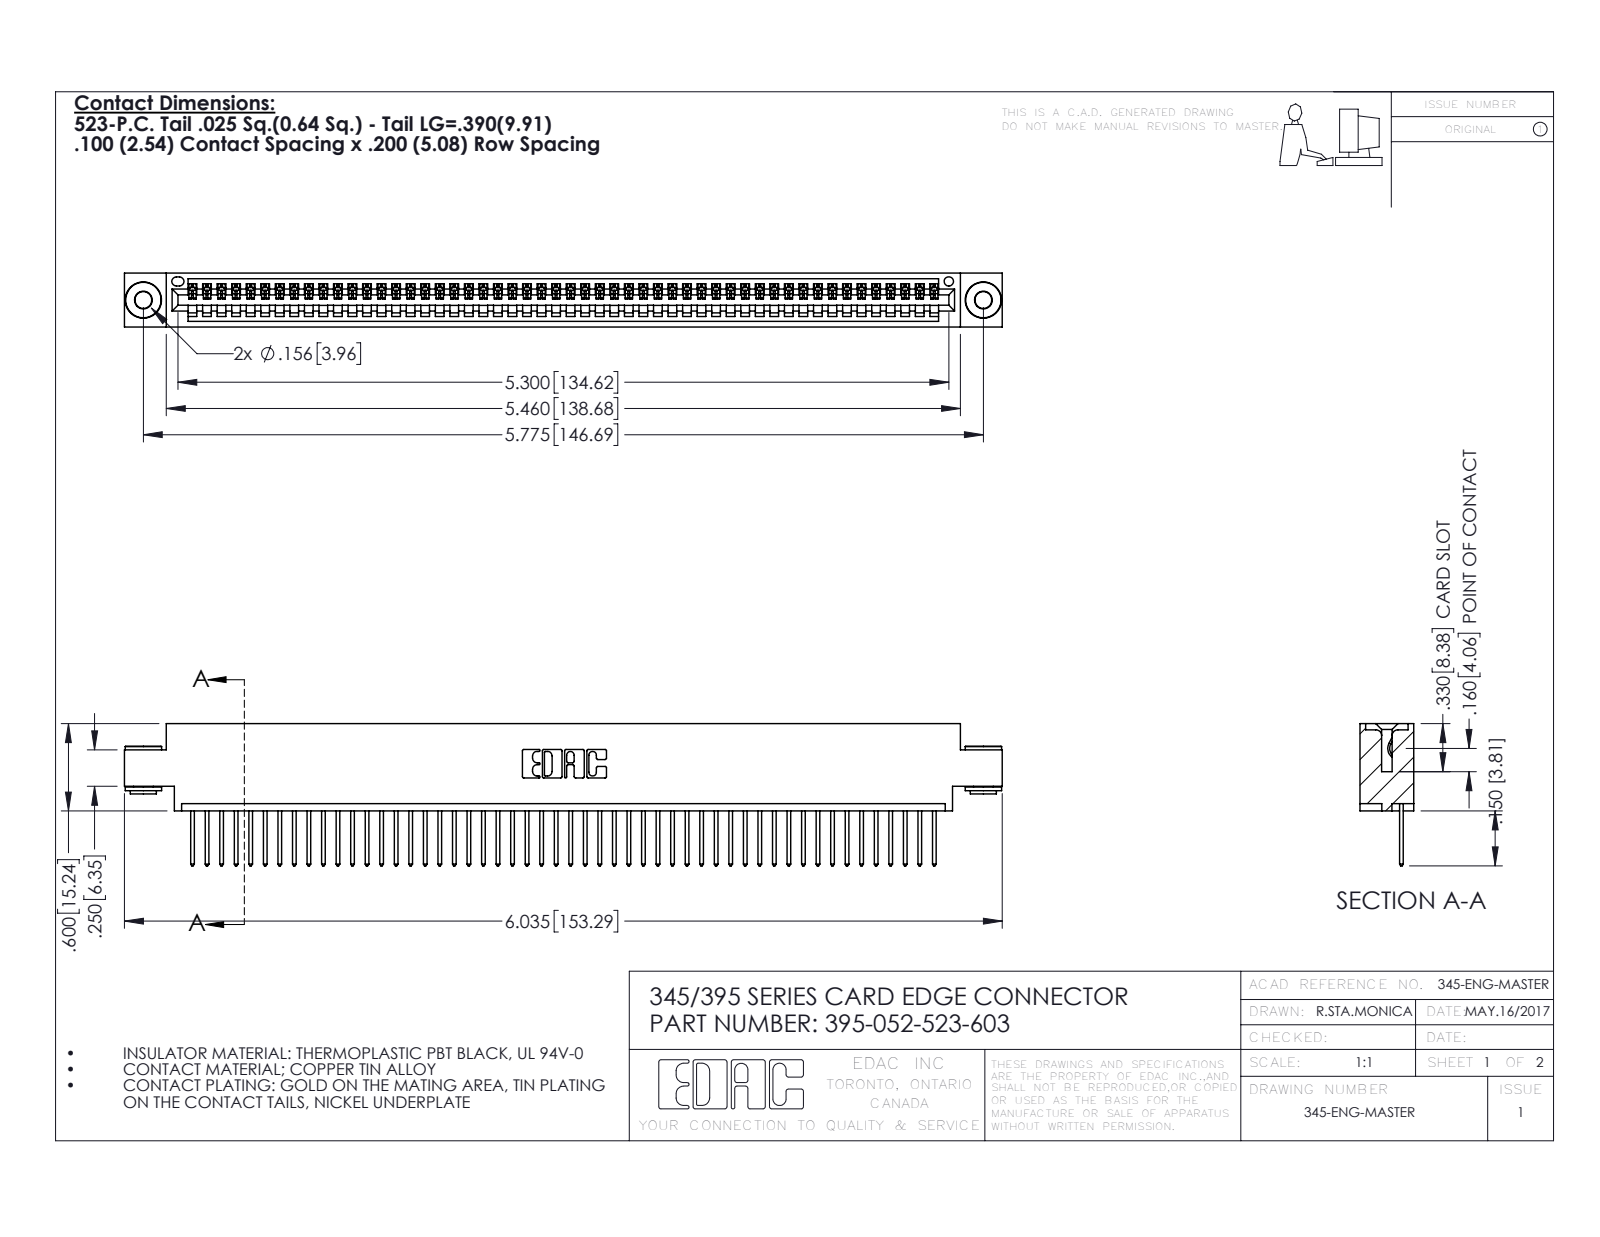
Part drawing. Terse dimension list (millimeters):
name: 395-052-523-603; 345 Part_0.170 Offset - 0.156 Dia-TH; 345-250-002_345-250-002-102; 345-292-001_345-293-123
written by: SolidWorks 2016 (CONFIG_CONTROL_DESIGN)
unit: mm
bodies: 55 solids, 3184 faces (2174 planar, 1002 cylindrical, 8 other)
size: 153.3 × 24.8 × 9.4
volume: 14 500 mm³; area: 19 840 mm²
holes: 2× ⌀2.9, 2× ⌀4, 1× ⌀1.6
bosses: 2× ⌀6.4, 2× ⌀4.6, 2× ⌀3.5
rounds: 104× R0.2, 104× R0.3, 22× R0.3, 6× R0.2, 6× R0.8, 3× R0.7, 2× R0.8, 2× R1
face distances: 1.8, 7.6, 9.4, 2.5, 6.9, 0.6, 5.1, 5.7, 4.4, 3.8
hole spacings: 6.9, 140.7, 146.7
